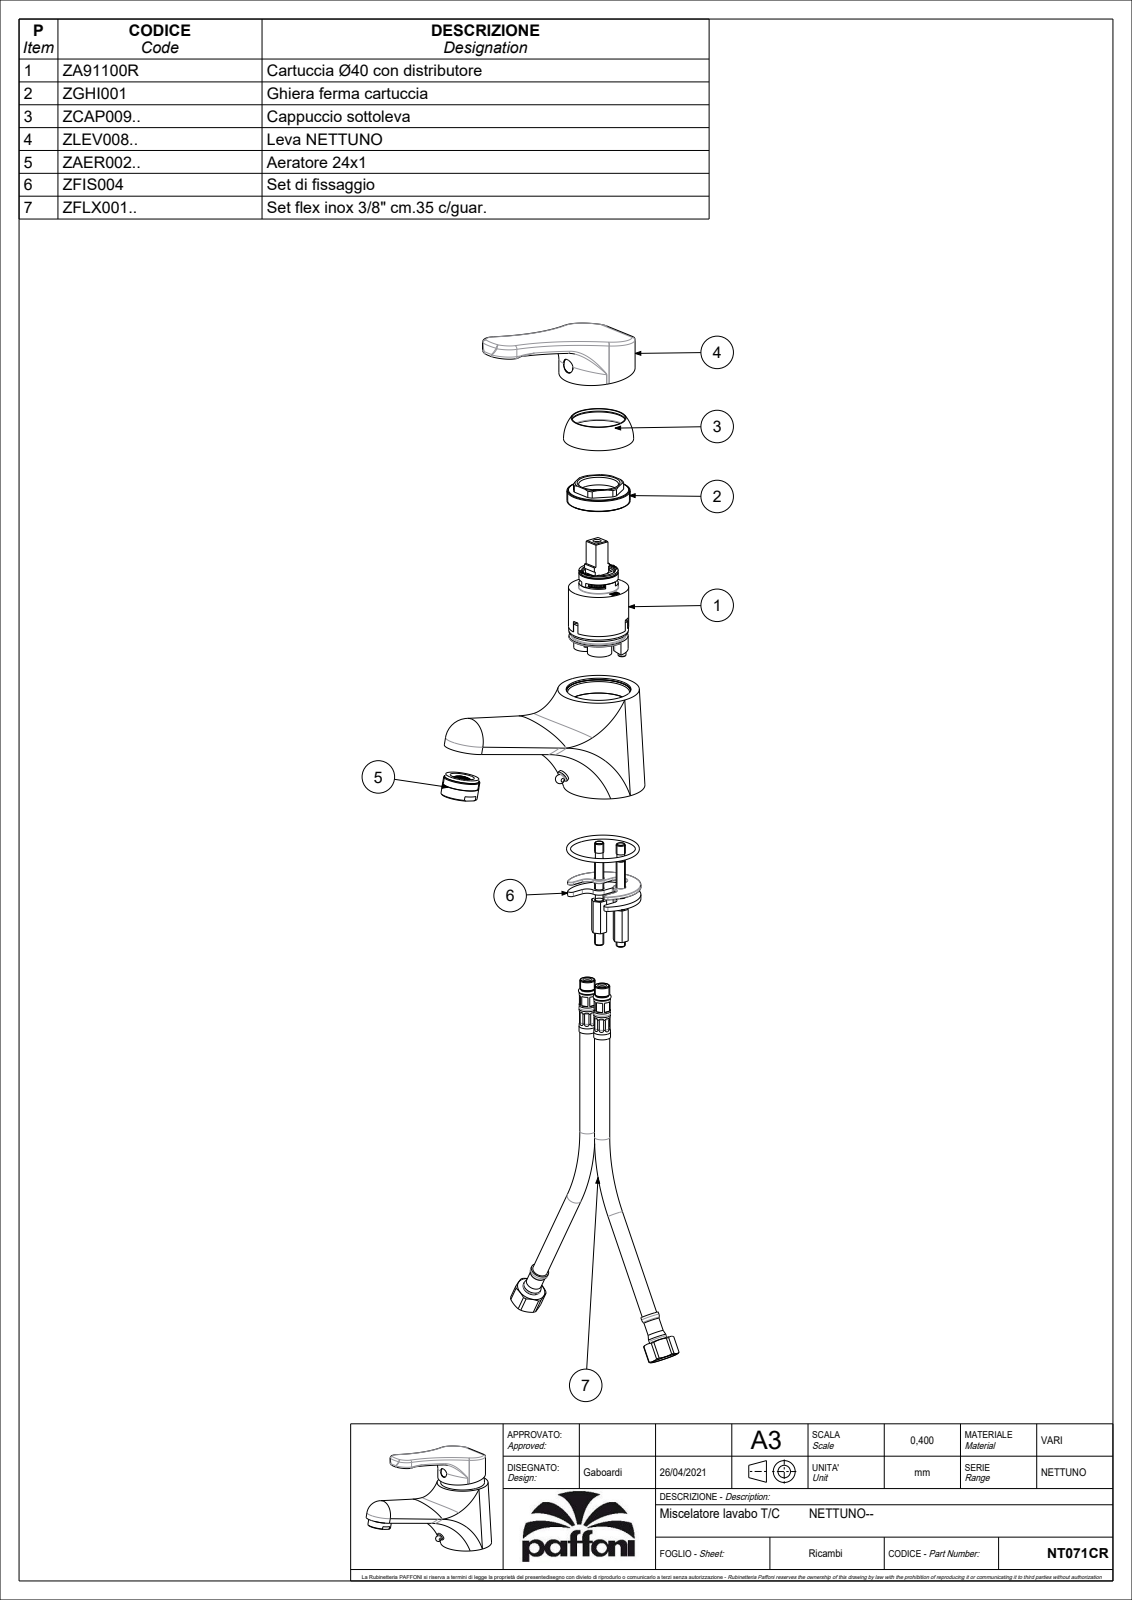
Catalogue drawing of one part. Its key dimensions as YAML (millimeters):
part_name: "NT071CR"
step_written_by: "CREO PARAMETRIC BY PTC INC, 2020044 (CONFIG_CONTROL_DESIGN)"
units: millimeters
bodies: {solids: 2, faces: 2677, planar: 1993, cylindrical: 378, other: 306}
overall_size: [158.92, 118.74, 53.5]
volume: 169228
surface_area: 95763
round_holes:
  - {diameter: 8, count: 4}
  - {diameter: 11, count: 3}
  - {diameter: 5.5, count: 2}
  - {diameter: 7, count: 2}
  - {diameter: 9, count: 2}
  - {diameter: 12, count: 2}
  - {diameter: 21, count: 2}
  - {diameter: 2.5, count: 1}
  - {diameter: 3.3, count: 1}
  - {diameter: 4, count: 1}
  - {diameter: 4.5, count: 1}
  - {diameter: 5, count: 1}
round_bosses_or_shafts:
  - {diameter: 15.9, count: 2}
  - {diameter: 10, count: 2}
  - {diameter: 9.4, count: 2}
  - {diameter: 8, count: 2}
  - {diameter: 50, count: 1}
  - {diameter: 41.7, count: 1}
  - {diameter: 39.5, count: 1}
  - {diameter: 39.2, count: 1}
partial_cylinders:
  - {radius: 0.5, count: 51}
  - {radius: 0.2, count: 24}
  - {radius: 1.5, count: 6}
  - {radius: 2, count: 6}
  - {radius: 1, count: 5}
  - {radius: 0.3, count: 4}
  - {radius: 7.5, count: 4}
  - {radius: 5.5, count: 2}
face_to_face_distances: [3.5, 6, 3, 4, 5, 10, 0.5, 7.95, 1.5, 22]
hole_center_spacings: [9.9, 1.12, 13.04, 14.53, 2, 7.92, 8.6, 8.85]
